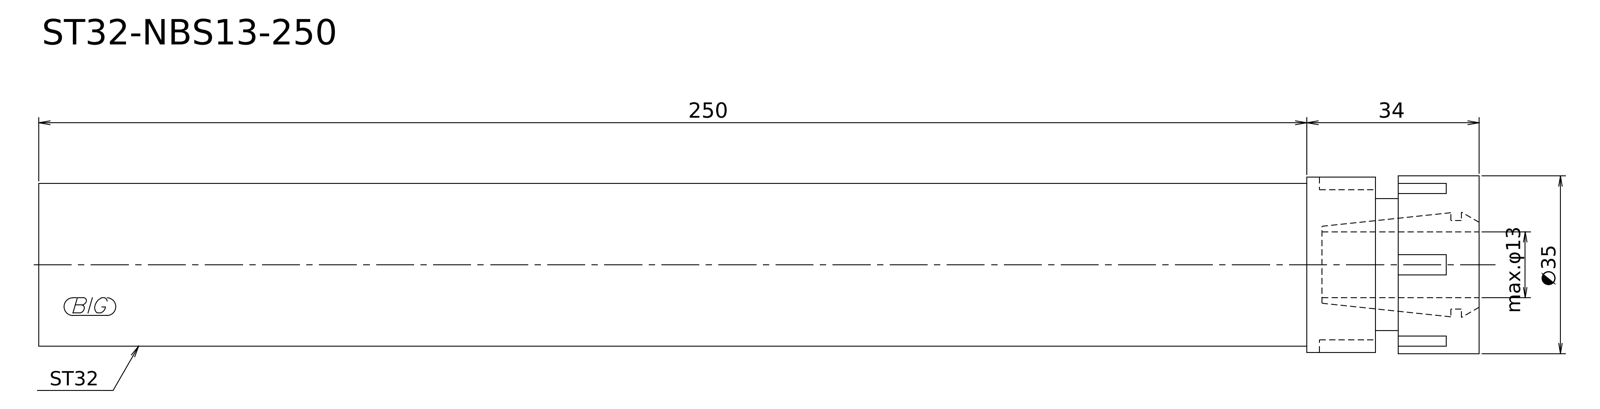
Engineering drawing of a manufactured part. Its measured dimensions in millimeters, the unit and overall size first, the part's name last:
Units: millimetres
Overall size (bounding box): 284 × 35 × 35
Round bosses / shafts (diameter × count): ⌀35 ×1, ⌀34.5 ×1, ⌀32 ×1, ⌀26 ×1
Main face-to-face distances: 284, 16, 268, 20.5, 4.5, 263.5, 34, 18, 13.5, 250
Volume: 231 465 mm³ · Surface area: 31 455 mm²
Bodies: 1 solid, 9 faces (5 planar, 4 cylindrical, 0 other)
STEP written by: Kubotek KeyCreator V8.5.1 (14335) (CONFIG_CONTROL_DESIGN)
